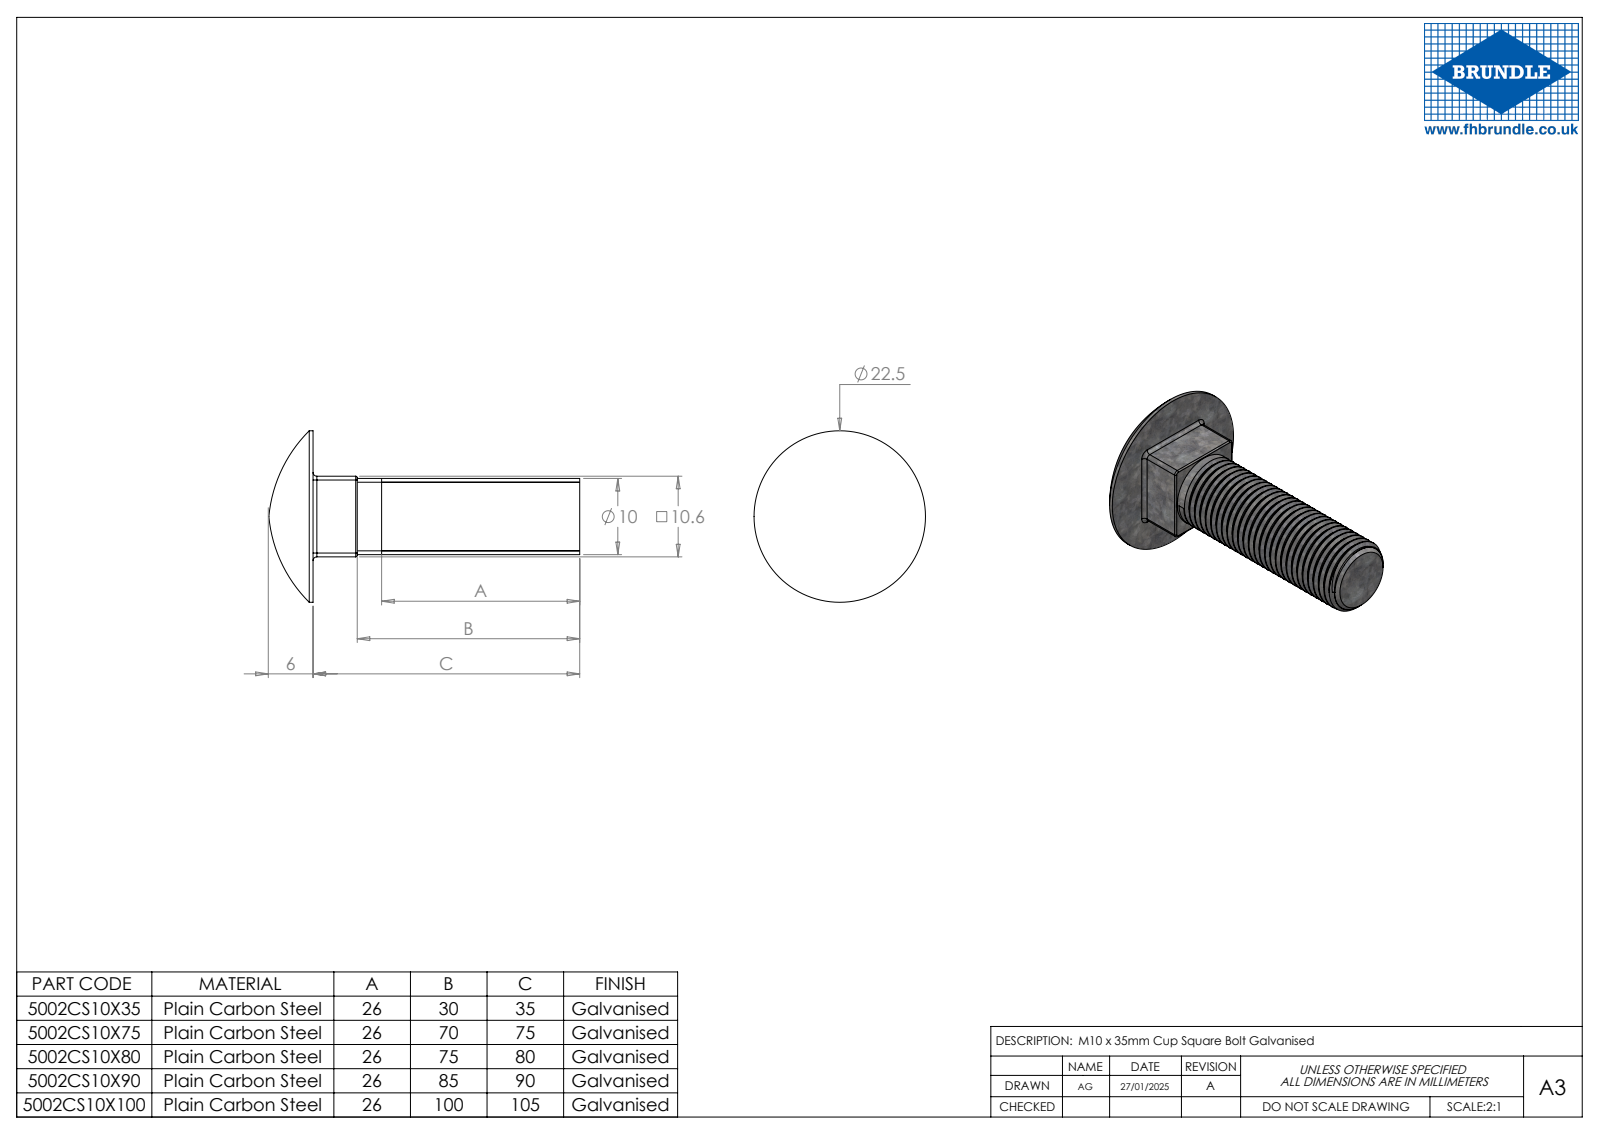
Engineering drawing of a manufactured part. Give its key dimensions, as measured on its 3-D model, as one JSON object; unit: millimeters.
{"part_name": "5002CS10X100", "step_written_by": "SolidWorks 2023 (CONFIG_CONTROL_DESIGN)", "units": "millimeters", "bodies": {"solids": 1, "faces": 33, "planar": 7, "cylindrical": 16, "other": 10}, "overall_size": [111.6, 22.5, 22.5], "volume_mm3": 9739, "surface_area_mm2": 4276, "round_bosses_or_shafts": [[22.5, 1], [10, 1]], "partial_cylinders_radius": [[0.5, 8], [0.2, 4]], "face_to_face_distances": [10.58, 105.8, 100, 5.8]}
